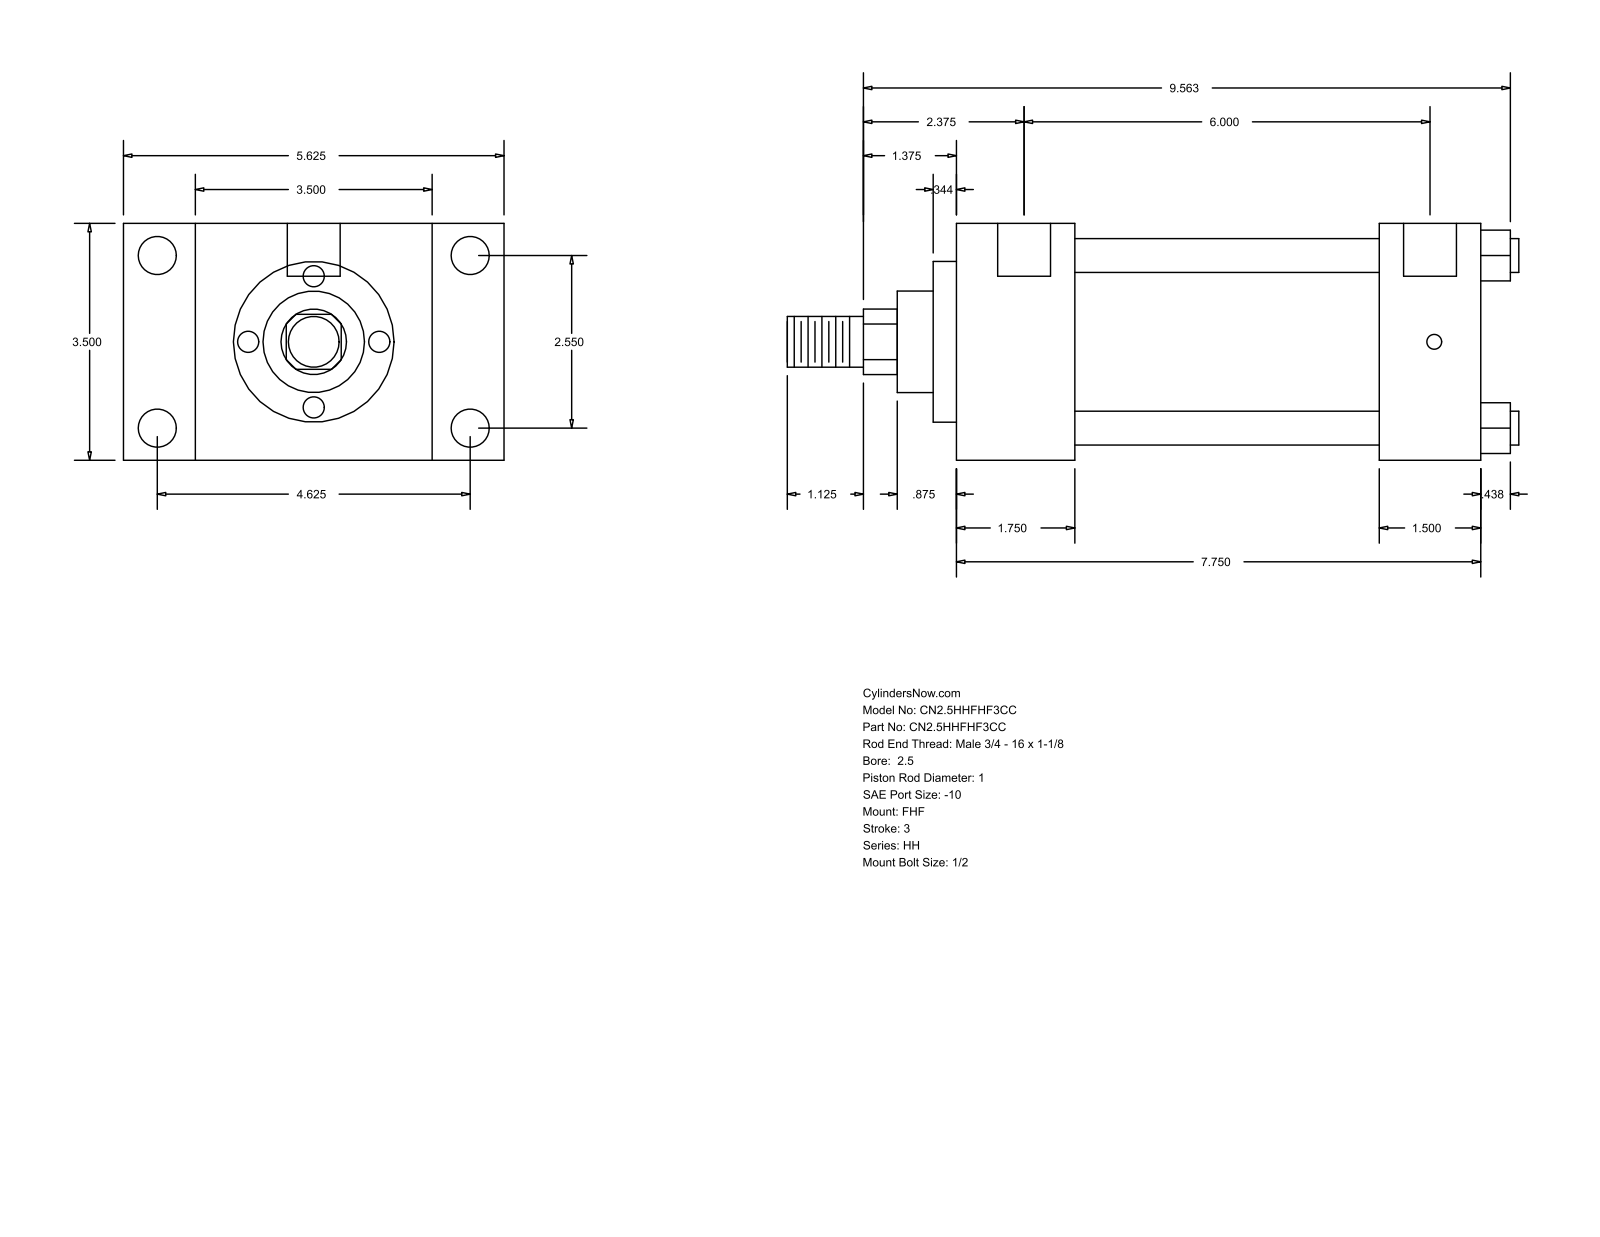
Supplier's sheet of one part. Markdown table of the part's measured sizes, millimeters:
| quantity | value |
| --- | --- |
| part name | HH_FHF__0250_1 |
| STEP written by | GSSL Pune (CONFIG_CONTROL_DESIGN) |
| units | millimeters |
| bodies | 0 solids, 90 faces (61 planar, 29 cylindrical, 0 other) |
| overall size | 274.64 × 142.88 × 88.9 |
| round holes (diameter × count) | 5.56 × 4, 14.3 × 4, 19.84 × 2 |
| round bosses / shafts (diameter × count) | 12.7 × 4, 73.03 × 1, 60.33 × 1, 38.1 × 1, 25.4 × 1, 19.05 × 1 |
| partial cylindrical surfaces (radius × count) | 12.29 × 1 |
| main face-to-face distances | 88.9, 44.46, 26.99, 115.89, 196.86, 152.4, 142.88, 38.1, 158.76, 114.3 |
| hole center spacings | 1.59, 64.76, 117.48, 134.15, 153.98, 155.57, 152.39 |
